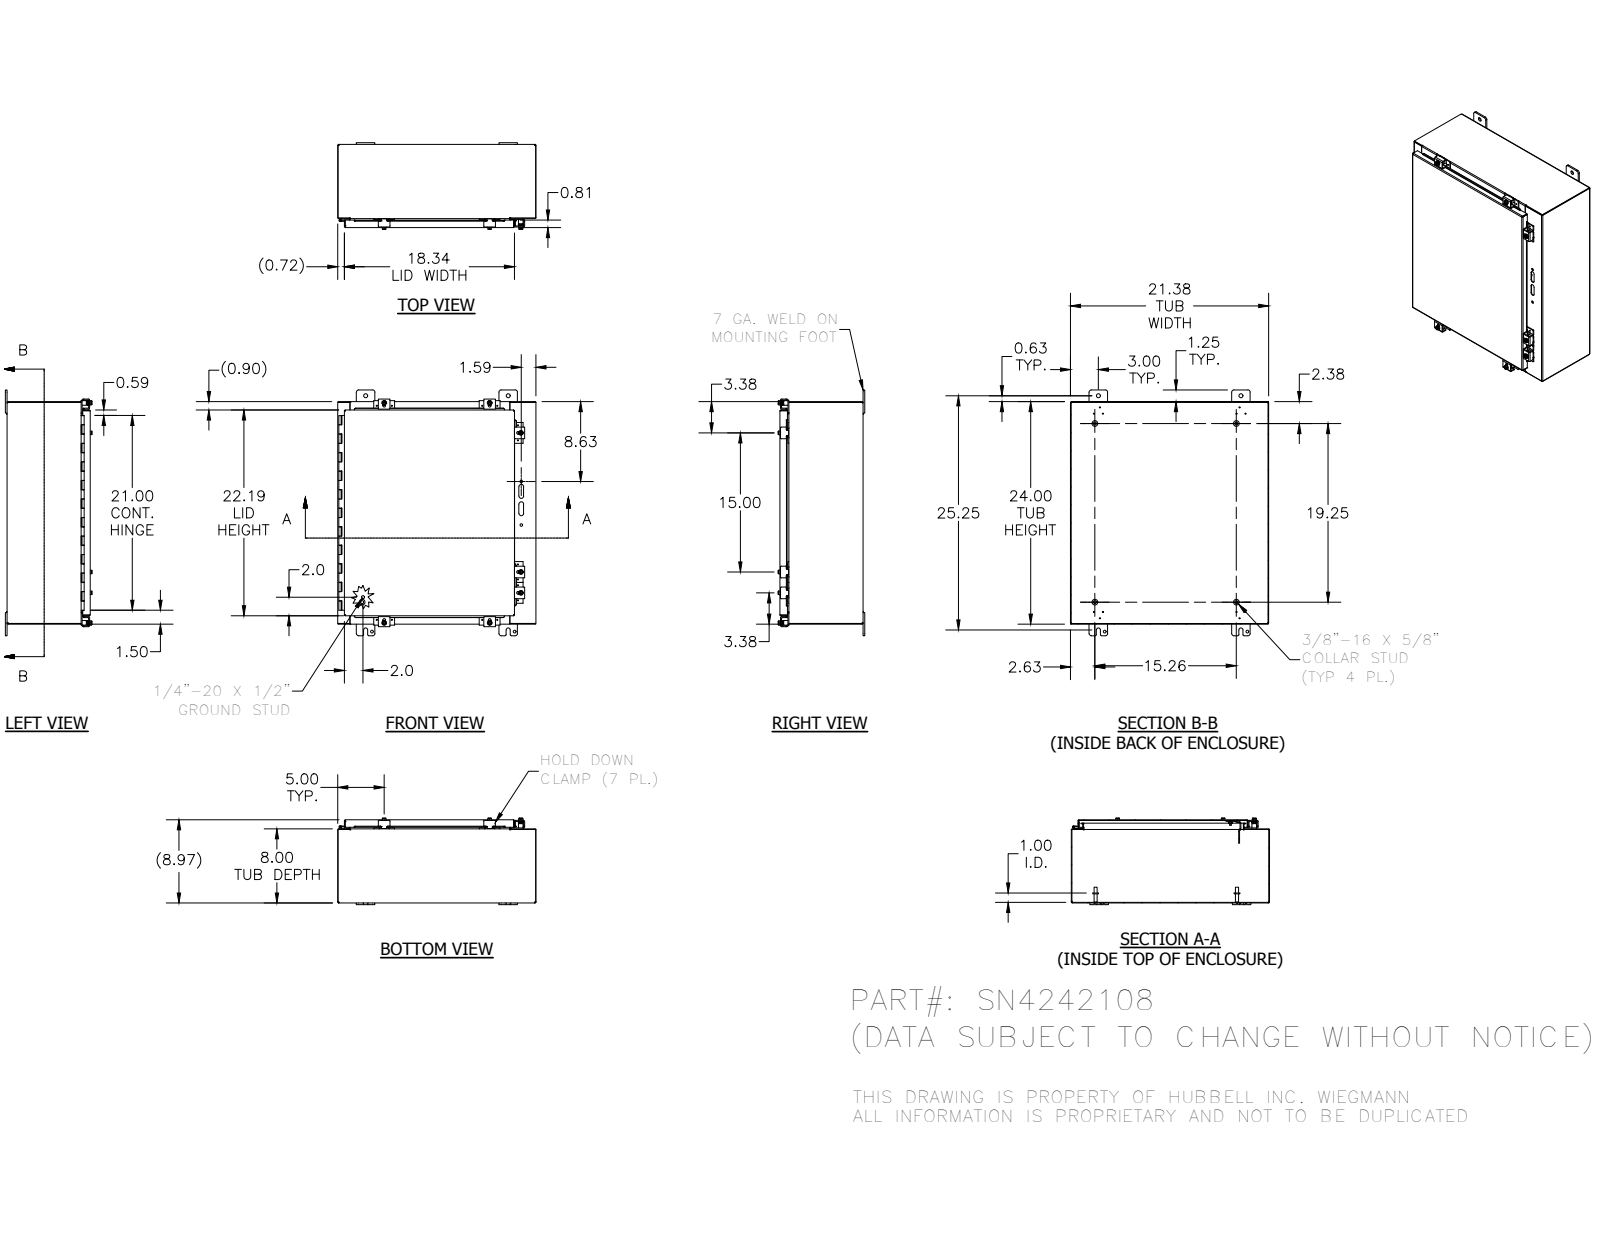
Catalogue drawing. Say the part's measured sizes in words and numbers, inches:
The part is named "SN4242108BKP; 388116; 34840; 328105T (+8 more)". Its 3-D file was written by "Autodesk Inventor 2016 (AUTOMOTIVE_DESIGN)". It is 54 solids with 1684 faces: 915 planar, 545 cylindrical and 224 other. Overall it measures 26.5 by 21.38 by 9.325 inches. Its volume is 151.3 cubic inches and its surface area 4 077 square inches. Round holes: 14 of diameter 0.11, 12 of diameter 0.12, 9 of diameter 0.281, 7 of diameter 0.211, 7 of diameter 0.3, 4 of diameter 0.313, 4 of diameter 0.438, 2 of diameter 0.156, 1 of diameter 0.125. Round bosses or shafts: 11 of diameter 0.25, 7 of diameter 0.52, 7 of diameter 0.5, 7 of diameter 0.35, 5 of diameter 0.33, 4 of diameter 0.625, 2 of diameter 0.19, 2 of diameter 0.115. Partial cylindrical surfaces (rounded edges, fillets, slot ends): 81 of radius 0.03, 47 of radius 0.063, 33 of radius 0.25, 28 of radius 0.125, 23 of radius 0.031, 23 of radius 0.105, 14 of radius 0.141, 10 of radius 0.1. The main face-to-face distances are 0.074, 8.897, 8.823, 8.971, 21.306, 23.926, 7.926, 0.971, 21.38, 21.232. The hole center spacings are 0.759, 0.876, 1.593, 14.752, 15.38, 21.38, 21.402, 22.068.
